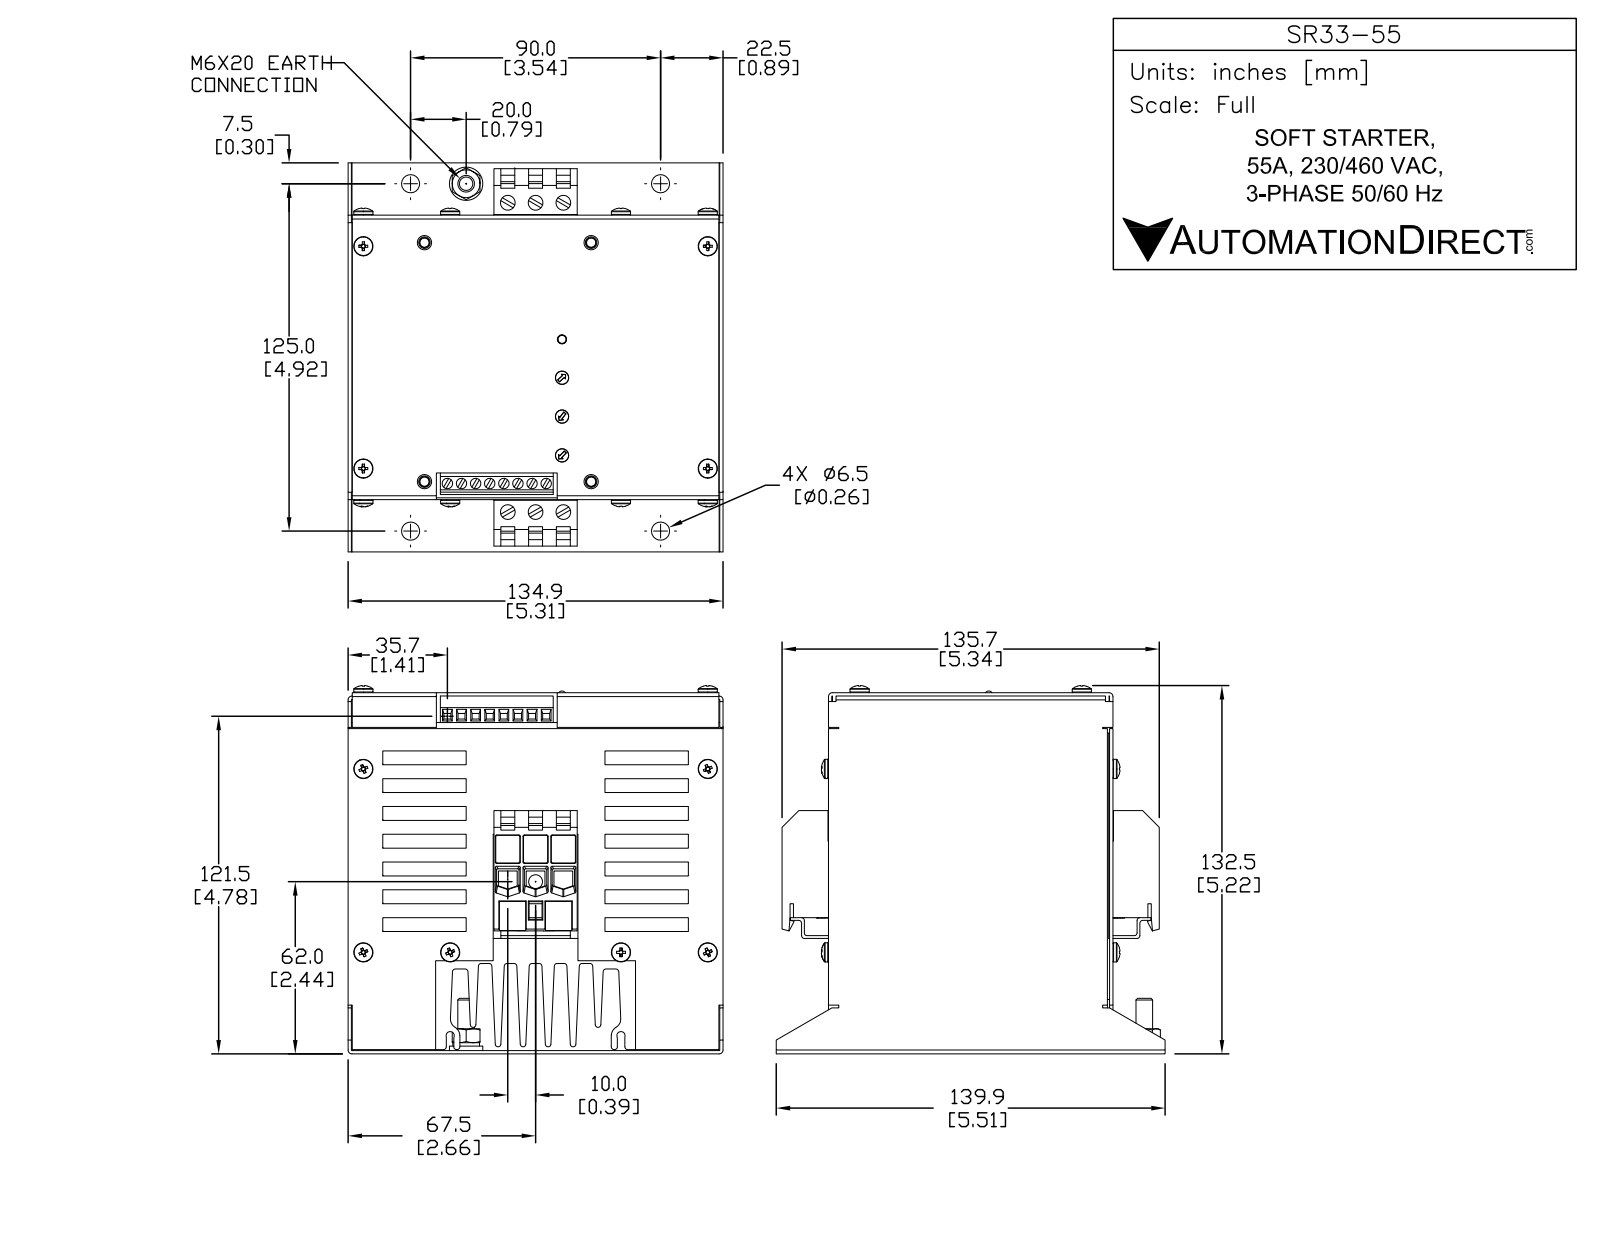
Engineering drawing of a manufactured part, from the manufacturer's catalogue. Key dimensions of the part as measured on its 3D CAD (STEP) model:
Part name (STEP PRODUCT): SR33-55
STEP written by: SolidWorks 2013 (AUTOMOTIVE_DESIGN)
Units: millimetres
Bodies: 1 solid, 980 faces (712 planar, 170 cylindrical, 98 other)
Overall size (bounding box): 139.9 × 134.9 × 132.9
Volume: 1 475 000 mm³ · Surface area: 260 135 mm²
Round holes (diameter × count): ⌀3.82 ×8, ⌀5 ×6, ⌀6.5 ×4
Round bosses / shafts (diameter × count): ⌀6.9 ×10, ⌀12 ×1, ⌀6 ×1
Partial cylindrical surfaces — rounded edges, fillets, slot ends (radius × count): R1 ×30, R0.44 ×14, R3 ×5, R2 ×4, R0.57 ×3, R0.5 ×2, R0.52 ×2, R0.52 ×2
Main face-to-face distances: 5, 10, 15, 20, 30, 25, 35, 40, 45, 50
Hole centre spacings: 10, 5, 20, 15, 35.55, 45.43, 55.35, 113.02
